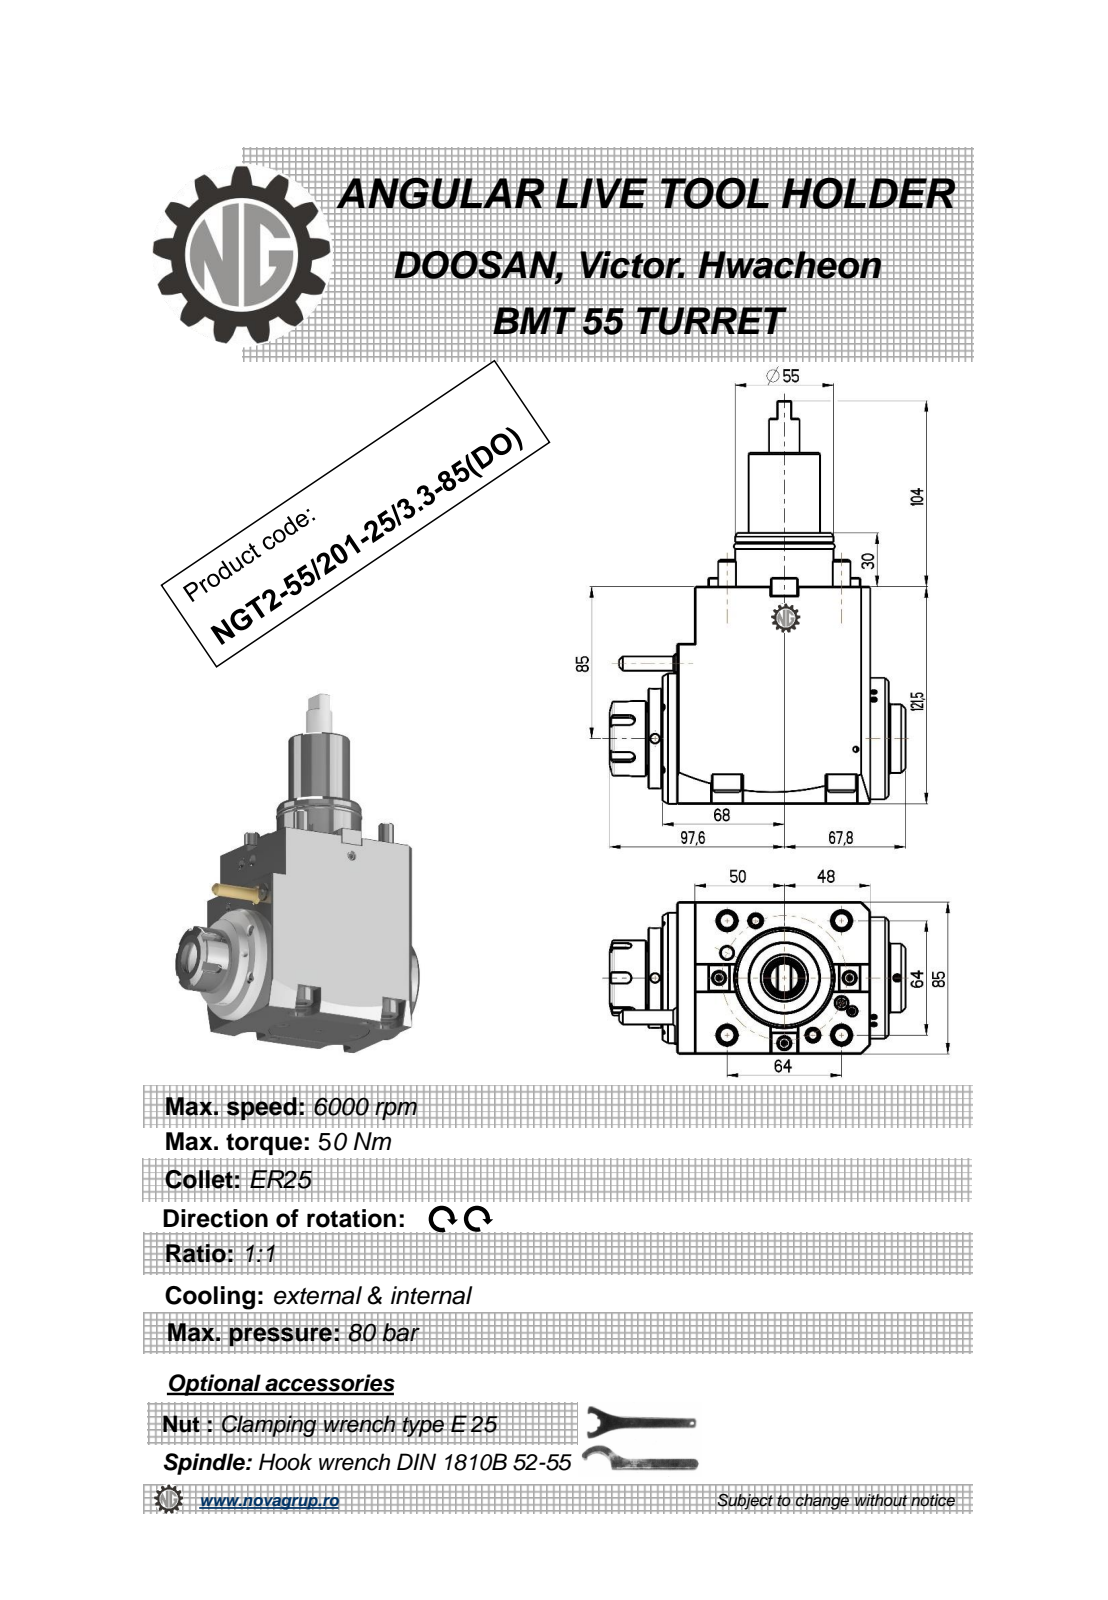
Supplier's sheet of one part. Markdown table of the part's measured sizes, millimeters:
| quantity | value |
| --- | --- |
| part name | NGT2_55_201_25_3_3_85_DO |
| STEP written by | PRO/ENGINEER BY PARAMETRIC TECHNOLOGY CORPORATION, 2010280 (CONFIG_CONTROL_DESIGN) |
| units | millimeters |
| bodies | 2 solids, 489 faces (229 planar, 111 cylindrical, 149 other) |
| overall size | 225.5 × 165.4 × 85 |
| volume | 1 323 000 mm³ |
| surface area | 114 291 mm² |
| round holes (diameter × count) | 5 × 3, 6.8 × 2, 3 × 1, 12 × 1 |
| round bosses / shafts (diameter × count) | 16 × 4, 10 × 4, 73 × 1, 68 × 1, 56 × 1, 55 × 1, 50 × 1, 43.4 × 1 |
| partial cylindrical surfaces (radius × count) | 0.32 × 20, 0.22 × 6, 3 × 5, 8.5 × 4, 0.8 × 2, 480 × 2 |
| main face-to-face distances | 85, 121.5, 8, 10, 108, 98, 18, 116, 108.3, 16 |
| hole center spacings | 42.62, 69.86, 105.19 |
